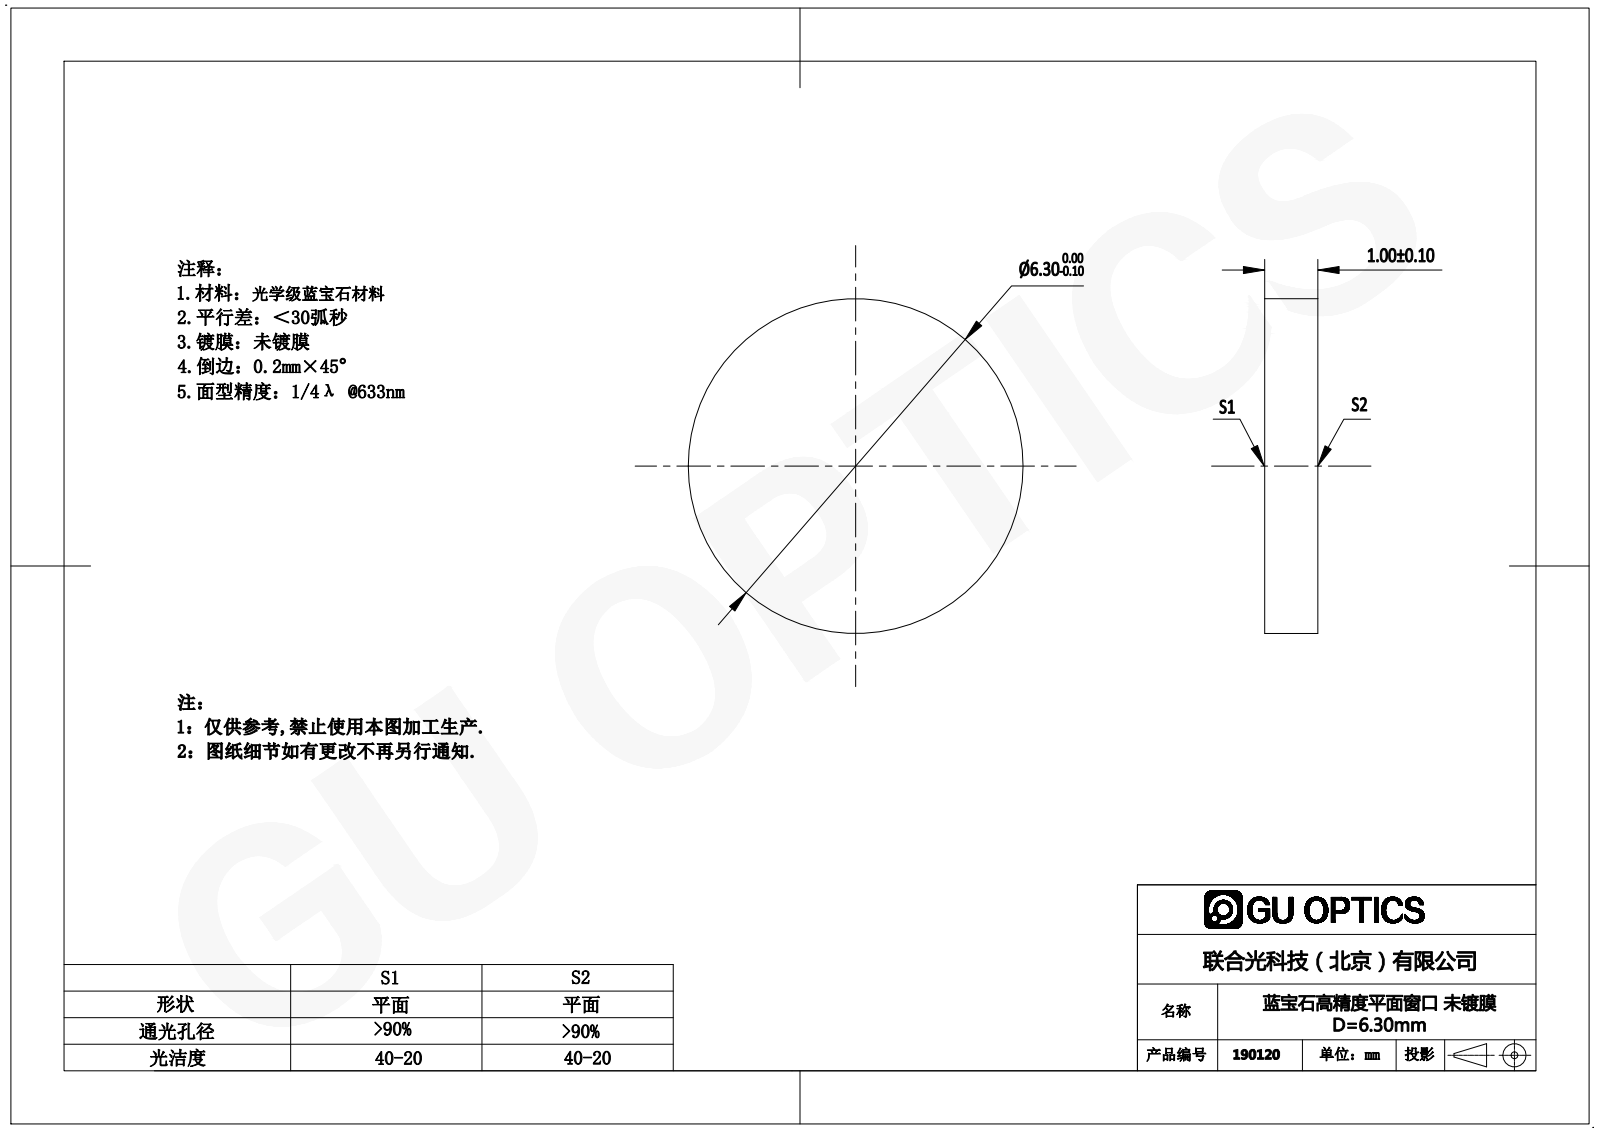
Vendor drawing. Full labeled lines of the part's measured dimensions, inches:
Part name (STEP PRODUCT): 190120
STEP written by: SolidWorks 2016 (AUTOMOTIVE_DESIGN)
Units: inches
Bodies: 1 solid, 4 faces (2 planar, 2 cylindrical, 0 other)
Overall size (bounding box): 0.248 × 0.248 × 0.039
Volume: 0.002 in³ · Surface area: 0.13 in²
Round bosses / shafts (diameter × count): ⌀0.248 ×1
Main face-to-face distances: 0.039
